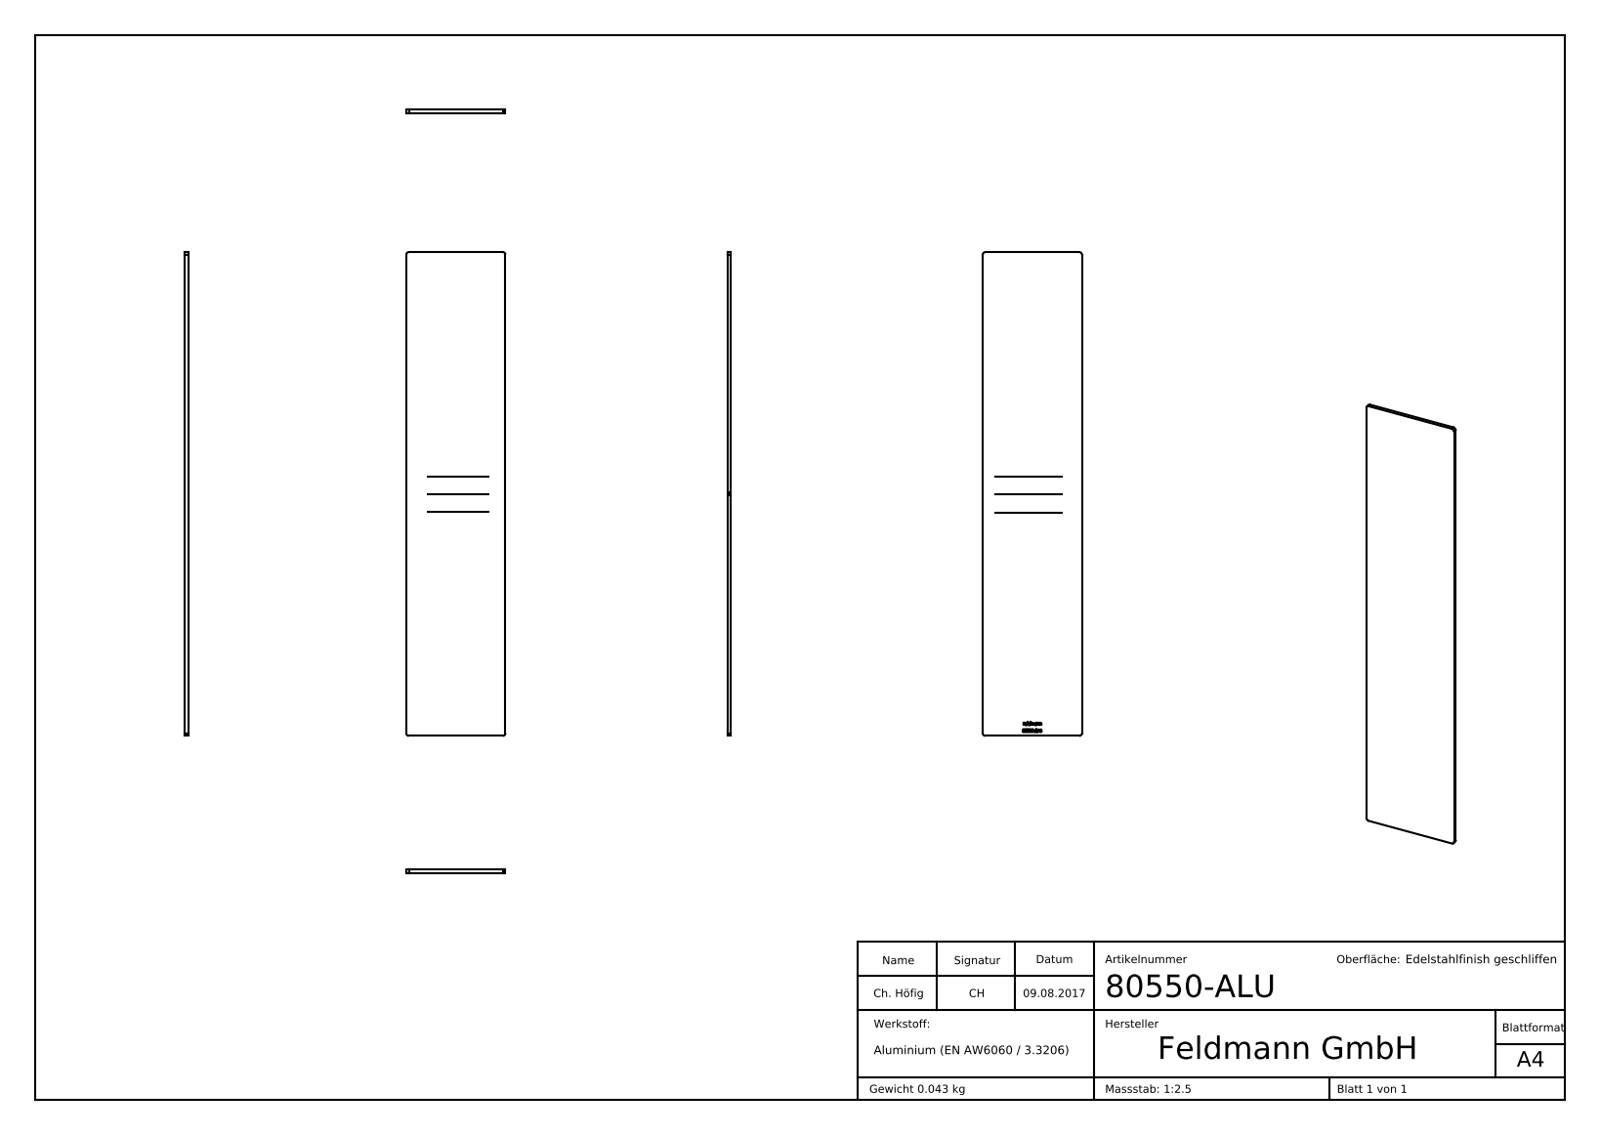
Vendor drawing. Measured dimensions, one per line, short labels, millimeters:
name: 80550-ALU
written by: SolidWorks 2015 (CONFIG_CONTROL_DESIGN)
unit: mm
bodies: 1 solid, 234 faces (124 planar, 4 cylindrical, 106 other)
size: 227 × 46.5 × 1.5
volume: 15 831 mm³; area: 21 936 mm²
rounds: 4× R1.2
face distances: 1.5, 46.5, 227, 1.4, 3.71, 3.66, 6.98, 3.27, 2.02, 0.74
